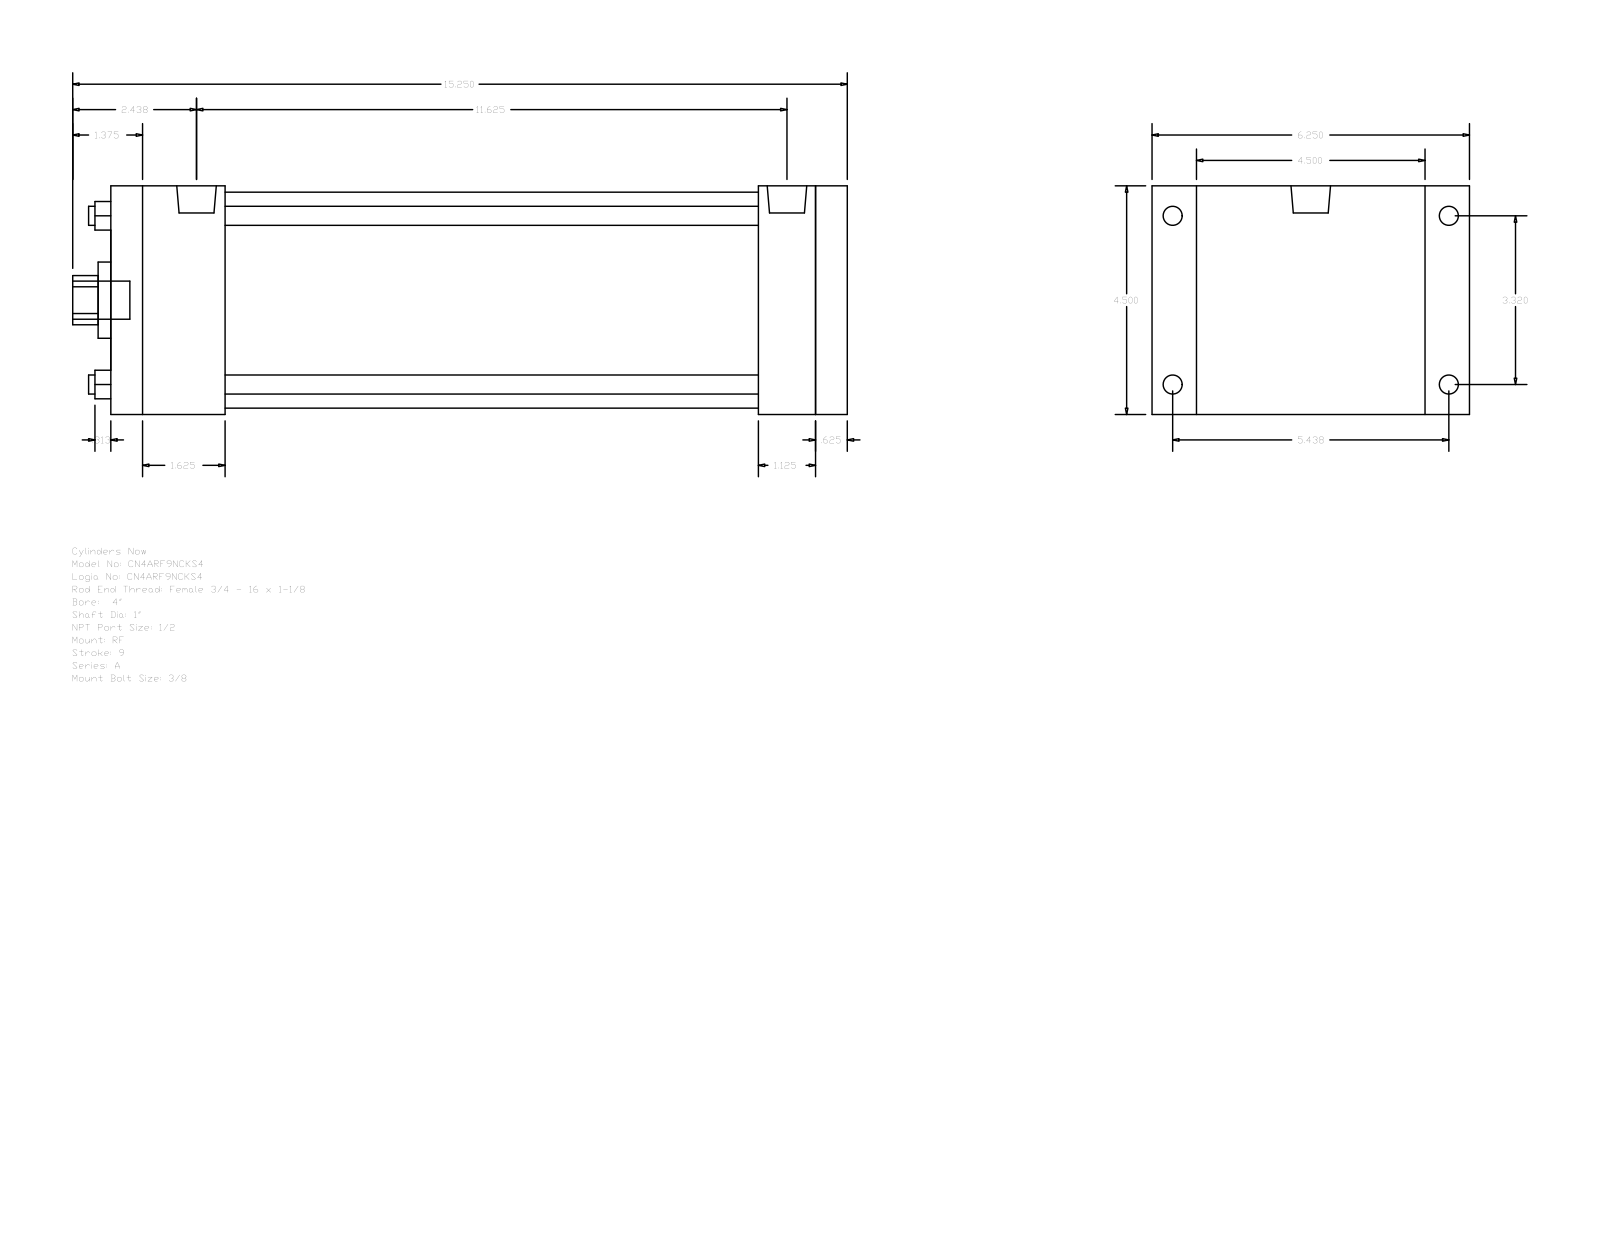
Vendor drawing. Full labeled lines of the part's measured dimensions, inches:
Part name (STEP PRODUCT): A_RF__0400_1
STEP written by: GSSL Pune (CONFIG_CONTROL_DESIGN)
Units: inches
Bodies: 0 solids, 92 faces (64 planar, 28 cylindrical, 0 other)
Overall size (bounding box): 15.25 × 6.25 × 4.5
Round holes (diameter × count): ⌀0.375 ×4, ⌀1 ×1, ⌀1.5 ×1, ⌀4.25 ×1
Round bosses / shafts (diameter × count): ⌀0.375 ×4, ⌀0.344 ×4, ⌀0.778 ×2, ⌀0.75 ×1
Partial cylindrical surfaces — rounded edges, fillets, slot ends (radius × count): R0.484 ×1
Main face-to-face distances: 4.5, 14.5, 0.625, 13.875, 0.875, 5.375, 12.75, 1.125, 1.75, 2.25
Hole centre spacings: 2.347, 3.32, 4.695
